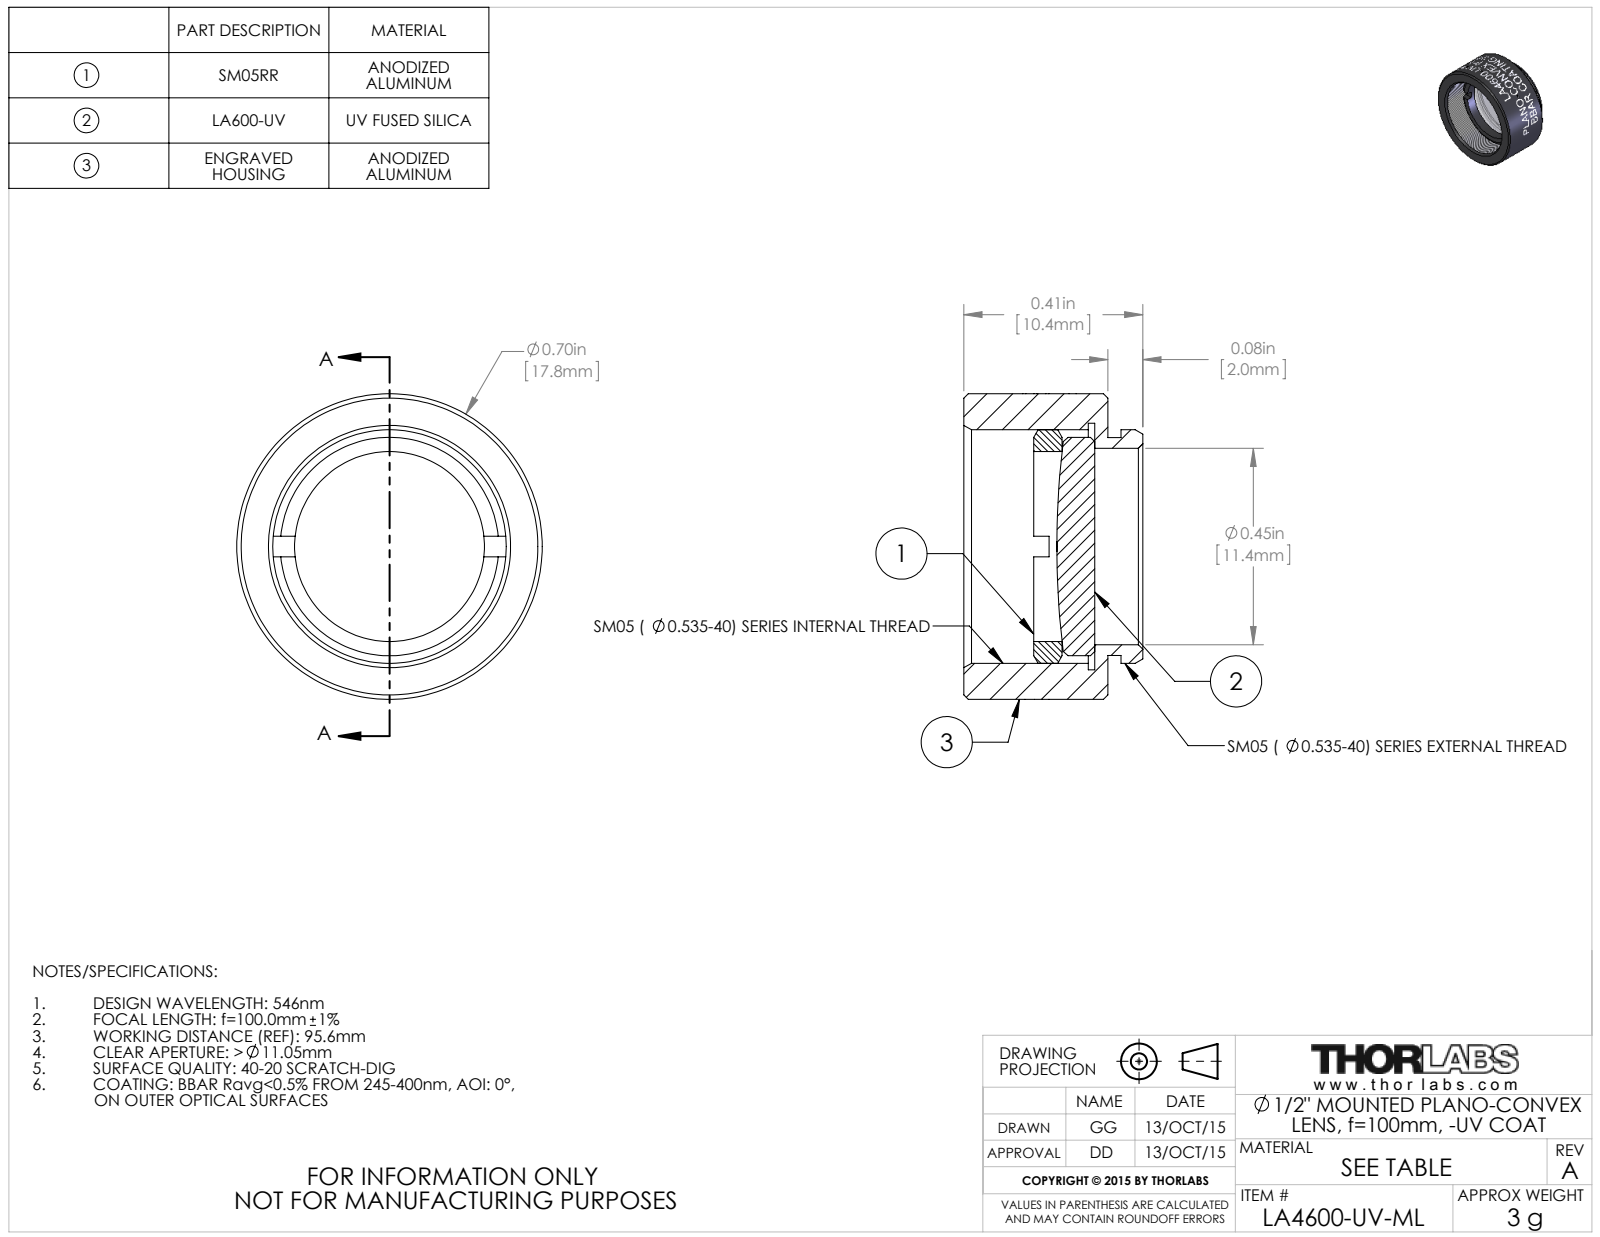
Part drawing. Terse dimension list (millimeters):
name: TTN039327-E0W
written by: SolidWorks 2014 (CONFIG_CONTROL_DESIGN)
unit: mm
bodies: 3 solids, 149 faces (16 planar, 112 cylindrical, 21 other)
size: 17.78 × 17.78 × 10.41
volume: 1 280 mm³; area: 1 829 mm²
holes: 1× ⌀11.05, 1× ⌀11.43, 1× ⌀13.59, 1× ⌀14.35
bosses: 1× ⌀17.78, 1× ⌀13.59, 1× ⌀12.7, 1× ⌀12.67
face distances: 0.76, 8.38, 7.62, 1.91, 1.52, 2.67, 5.71, 4.32, 3.56, 1.65
